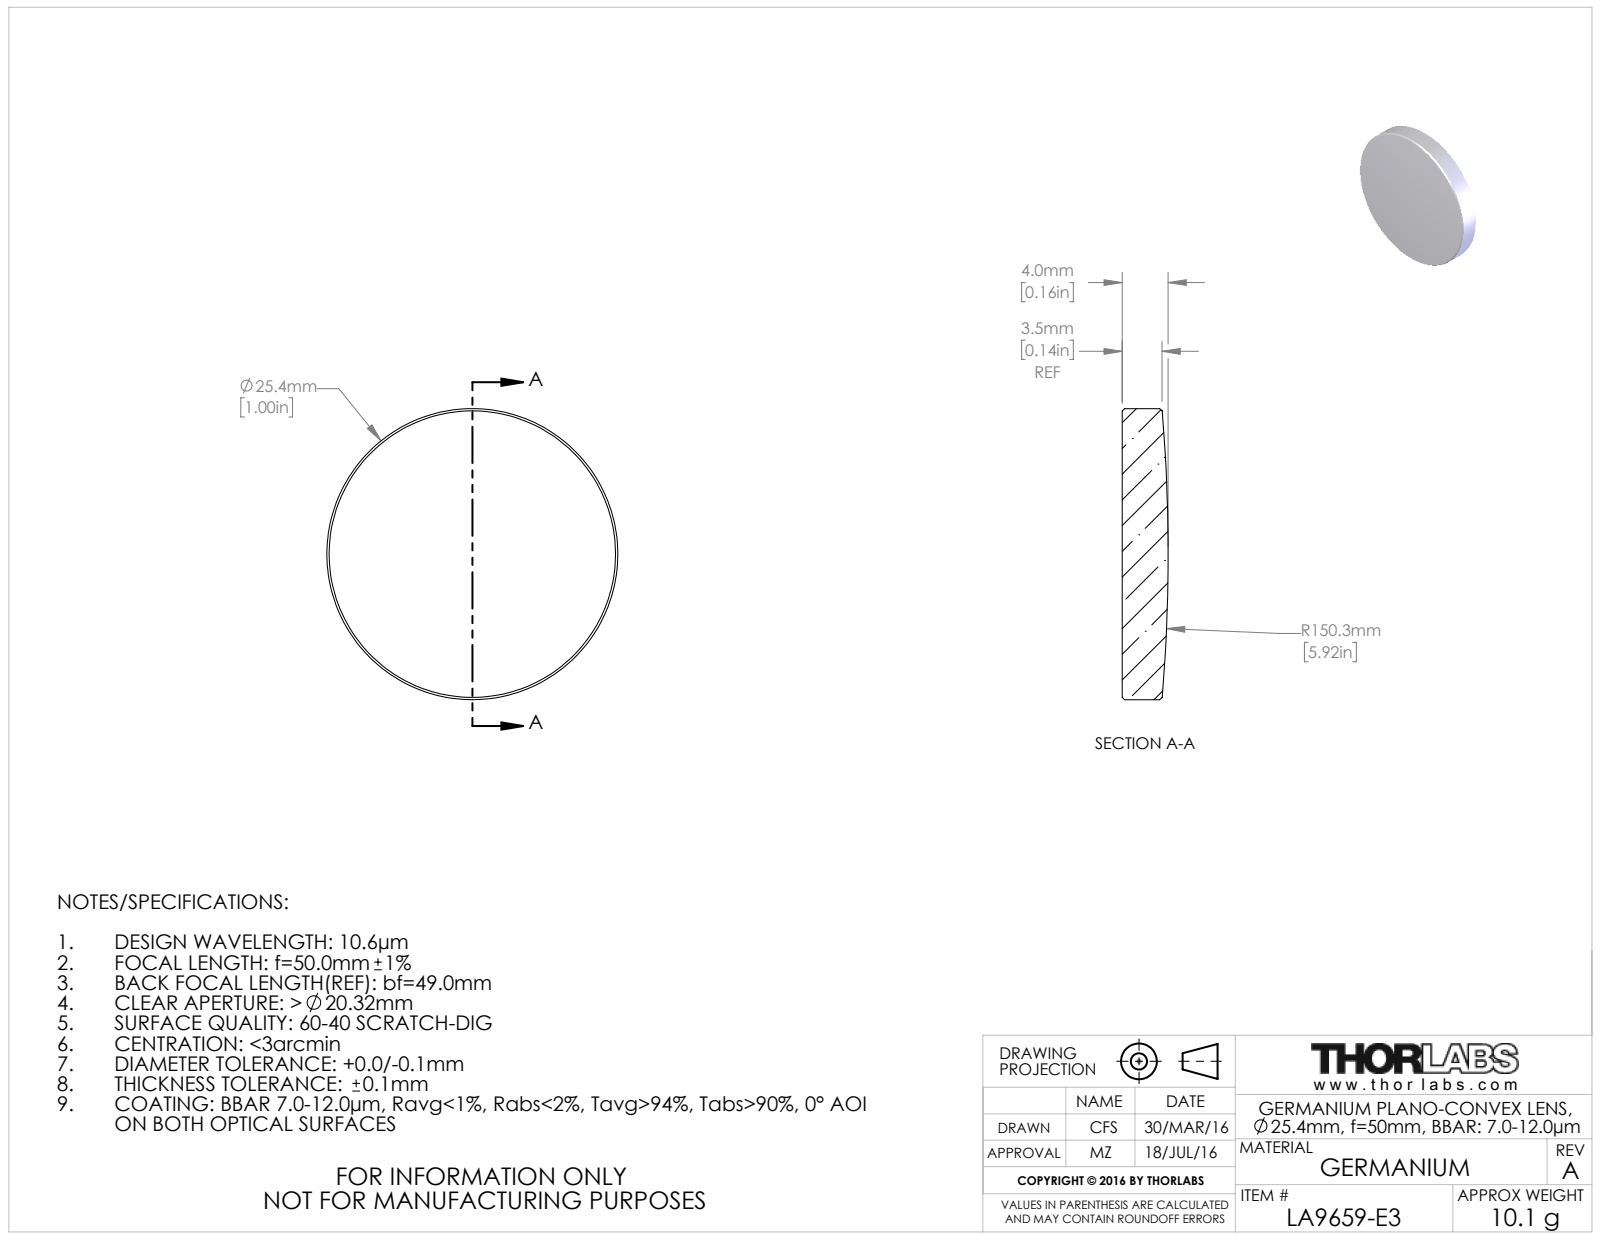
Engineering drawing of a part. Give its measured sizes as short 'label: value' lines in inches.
name: TTN049372-E0W
written by: SolidWorks 2016 (CONFIG_CONTROL_DESIGN)
unit: in
bodies: 1 solid, 9 faces (1 planar, 2 cylindrical, 6 other)
size: 1 × 1 × 0.157
volume: 0.115 in³; area: 1.973 in²
bosses: 1× ⌀1
